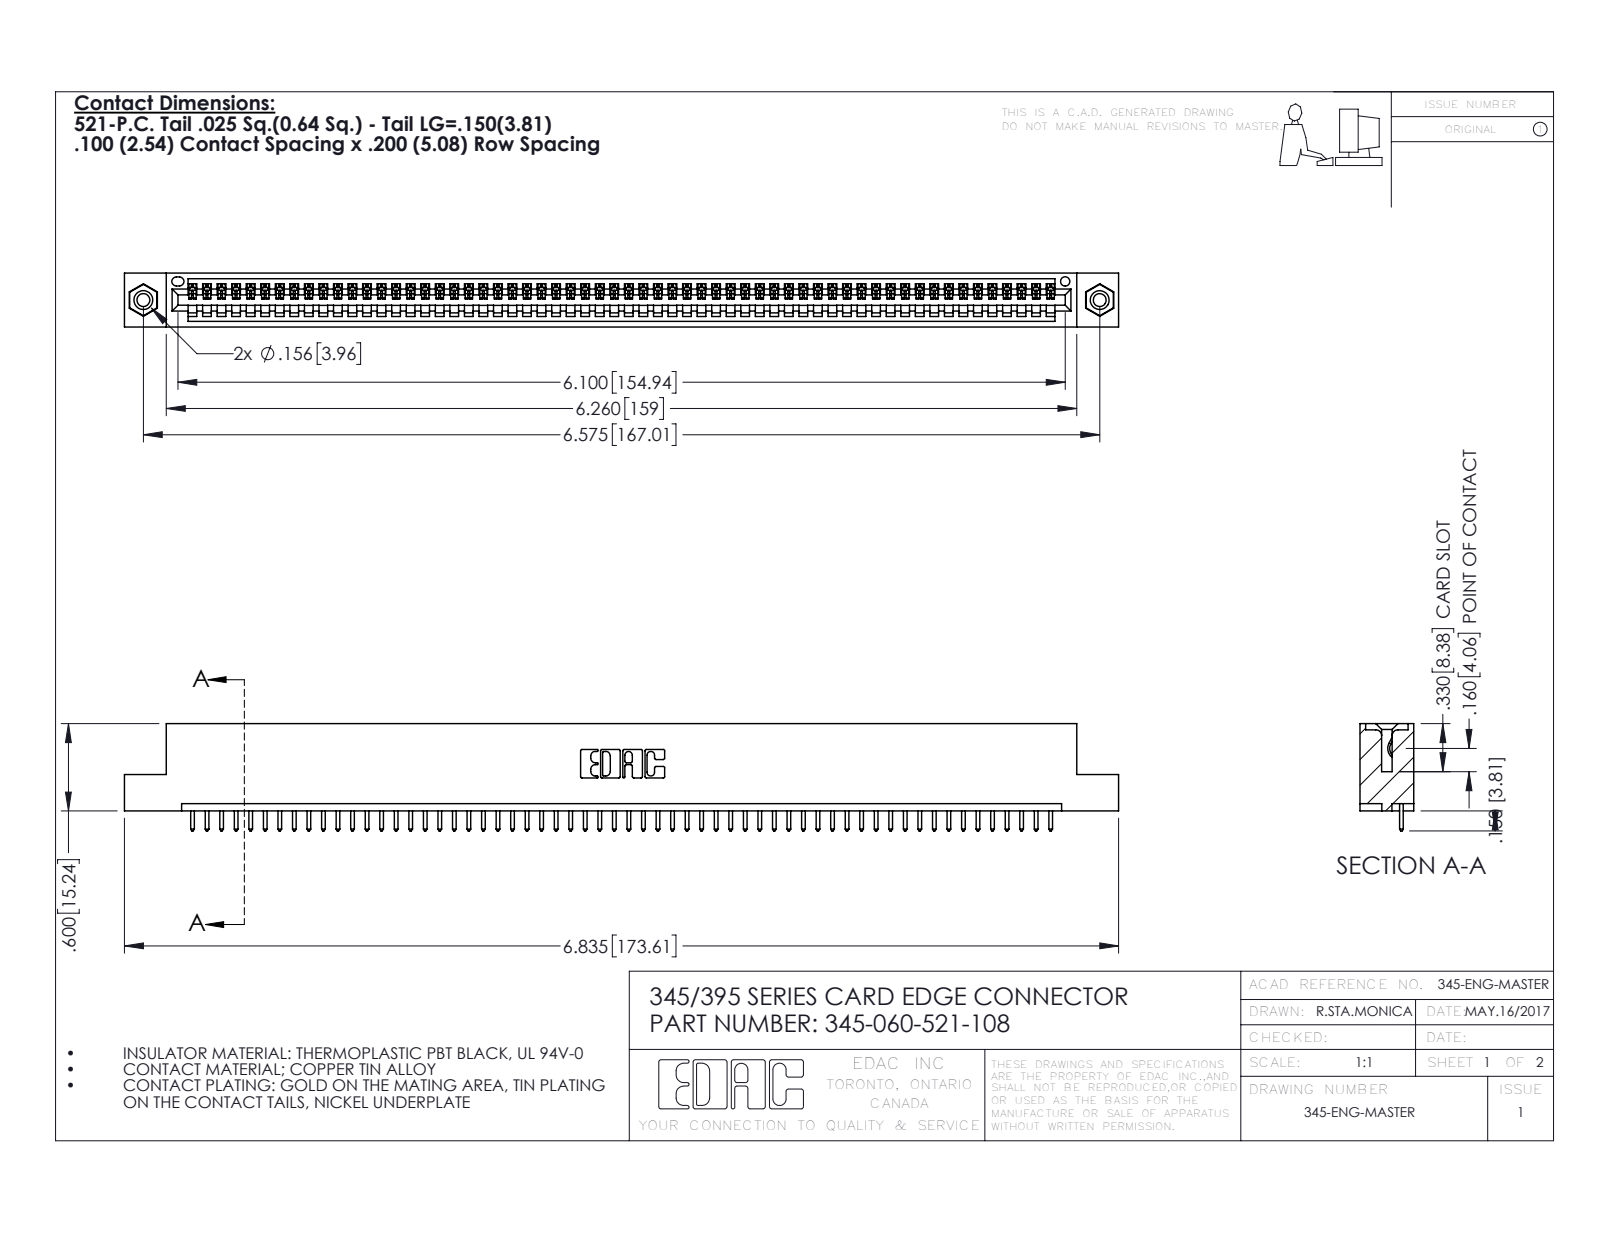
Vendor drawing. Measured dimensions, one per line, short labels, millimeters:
name: 345-250-001_345-250-003-102; 345-060-521-108; 345 Part_Flush Mounting Lugs - 0.156 Dia-TI; 345-292-001_345-293-121
written by: SolidWorks 2016 (CONFIG_CONTROL_DESIGN)
unit: mm
bodies: 63 solids, 3666 faces (2512 planar, 1138 cylindrical, 16 other)
size: 173.6 × 18.7 × 9.4
volume: 16 450 mm³; area: 21 470 mm²
holes: 2× ⌀2.3, 2× ⌀3.2, 2× ⌀4, 1× ⌀1.6
bosses: 2× ⌀3.9
rounds: 120× R0.2, 120× R0.3, 22× R0.3, 6× R0.2, 6× R0.8, 3× R0.7, 2× R0.8, 2× R1
face distances: 1.8, 7.6, 9.4, 5.1, 2.5, 6.9, 0.6, 5.7, 3.8, 1.8
hole spacings: 6.9, 161, 167
